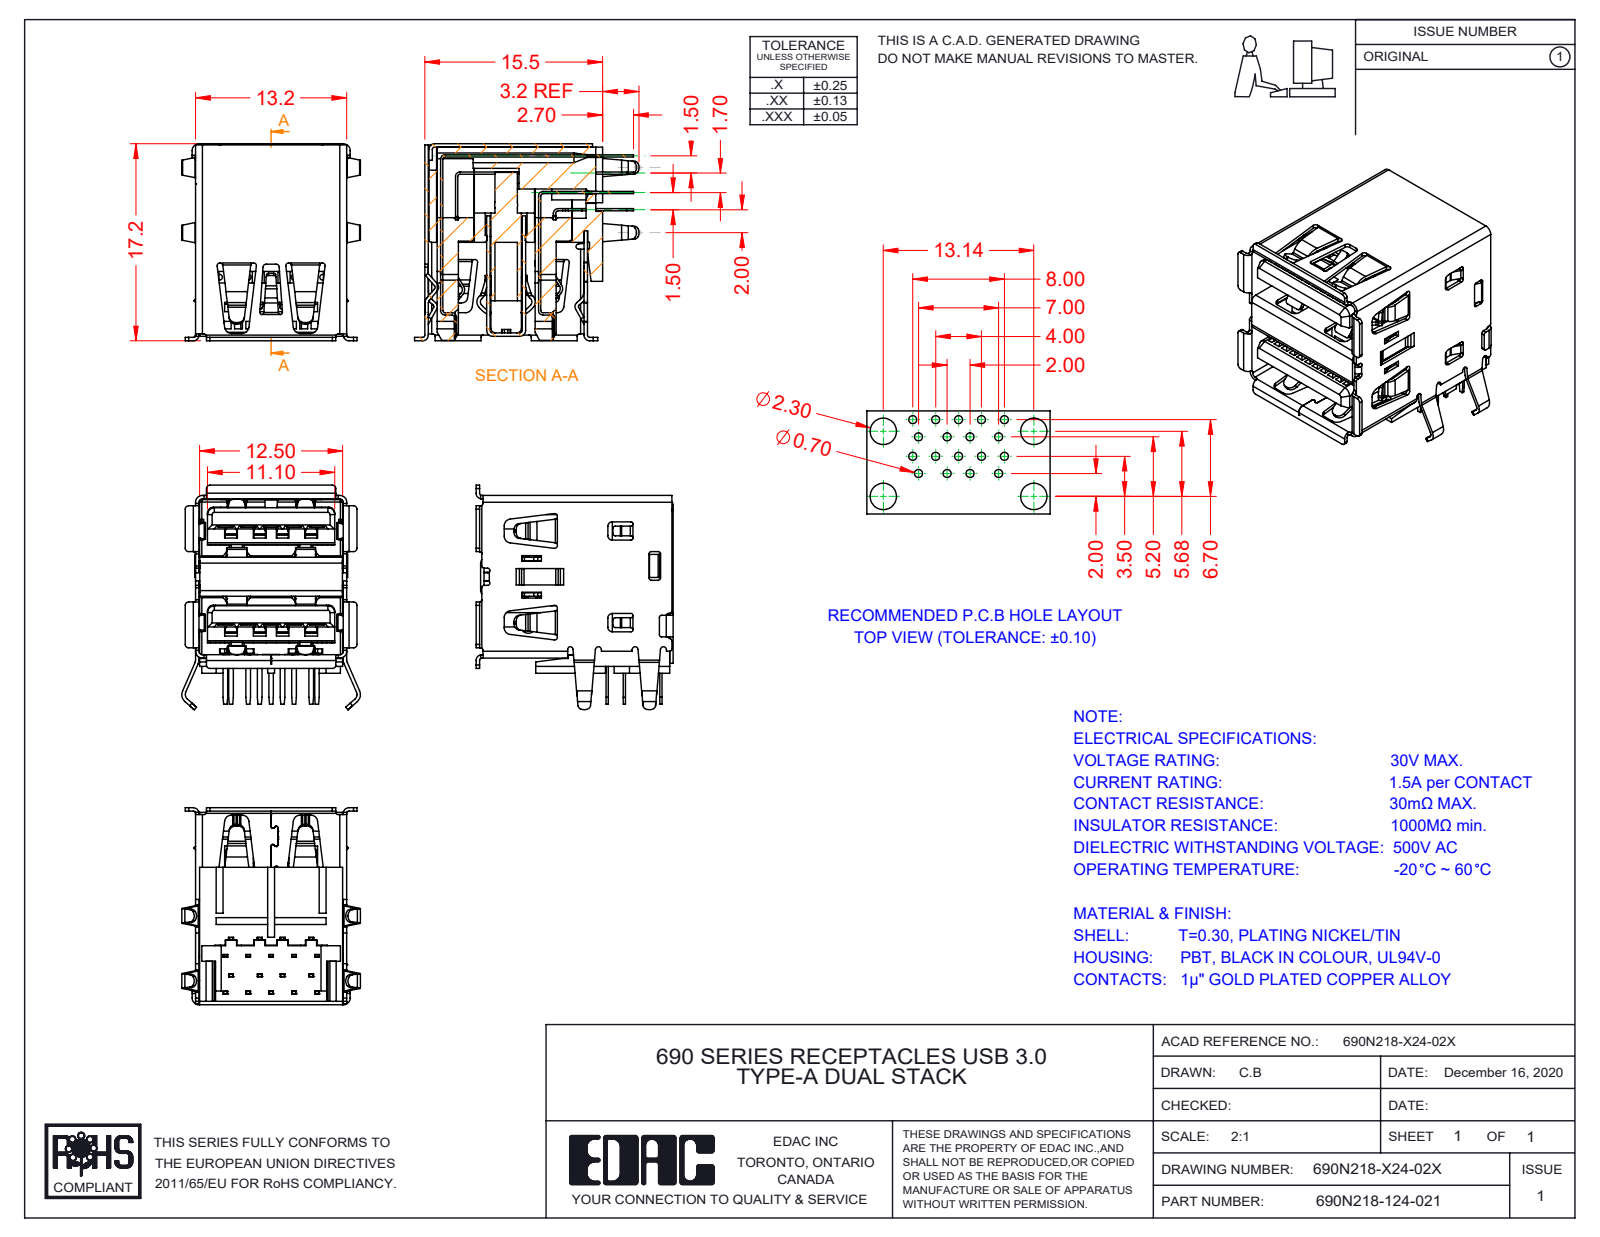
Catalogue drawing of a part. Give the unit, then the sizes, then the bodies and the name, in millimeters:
Units: millimetres
Overall size (bounding box): 19.6 × 17.2 × 15.6
Round holes (diameter × count): ⌀0.5 ×5
Partial cylindrical surfaces — rounded edges, fillets, slot ends (radius × count): R0.2 ×90, R0.5 ×72, R0.3 ×54, R0.15 ×50, R0.4 ×39, R0.6 ×34, R0.1 ×30, R1 ×20
Main face-to-face distances: 0.5, 12.9, 1.35, 1.7, 5.4, 8.5, 0.85, 0.7, 0.8, 0.35
Hole centre spacings: 2, 2.5, 4.5, 6.5, 4, 9
Volume: 1 707 mm³ · Surface area: 7 379 mm²
Bodies: 25 solids, 3066 faces (2258 planar, 788 cylindrical, 20 other)
Part name (STEP PRODUCT): Contact 9 690N218-X24-02X; Contact 18 690N218-X24-02X; Shell1 690N218-X24-02X; Contact 8 690N218-X24-02X (+8 more)
STEP written by: SolidWorks 2020 (AUTOMOTIVE_DESIGN)
